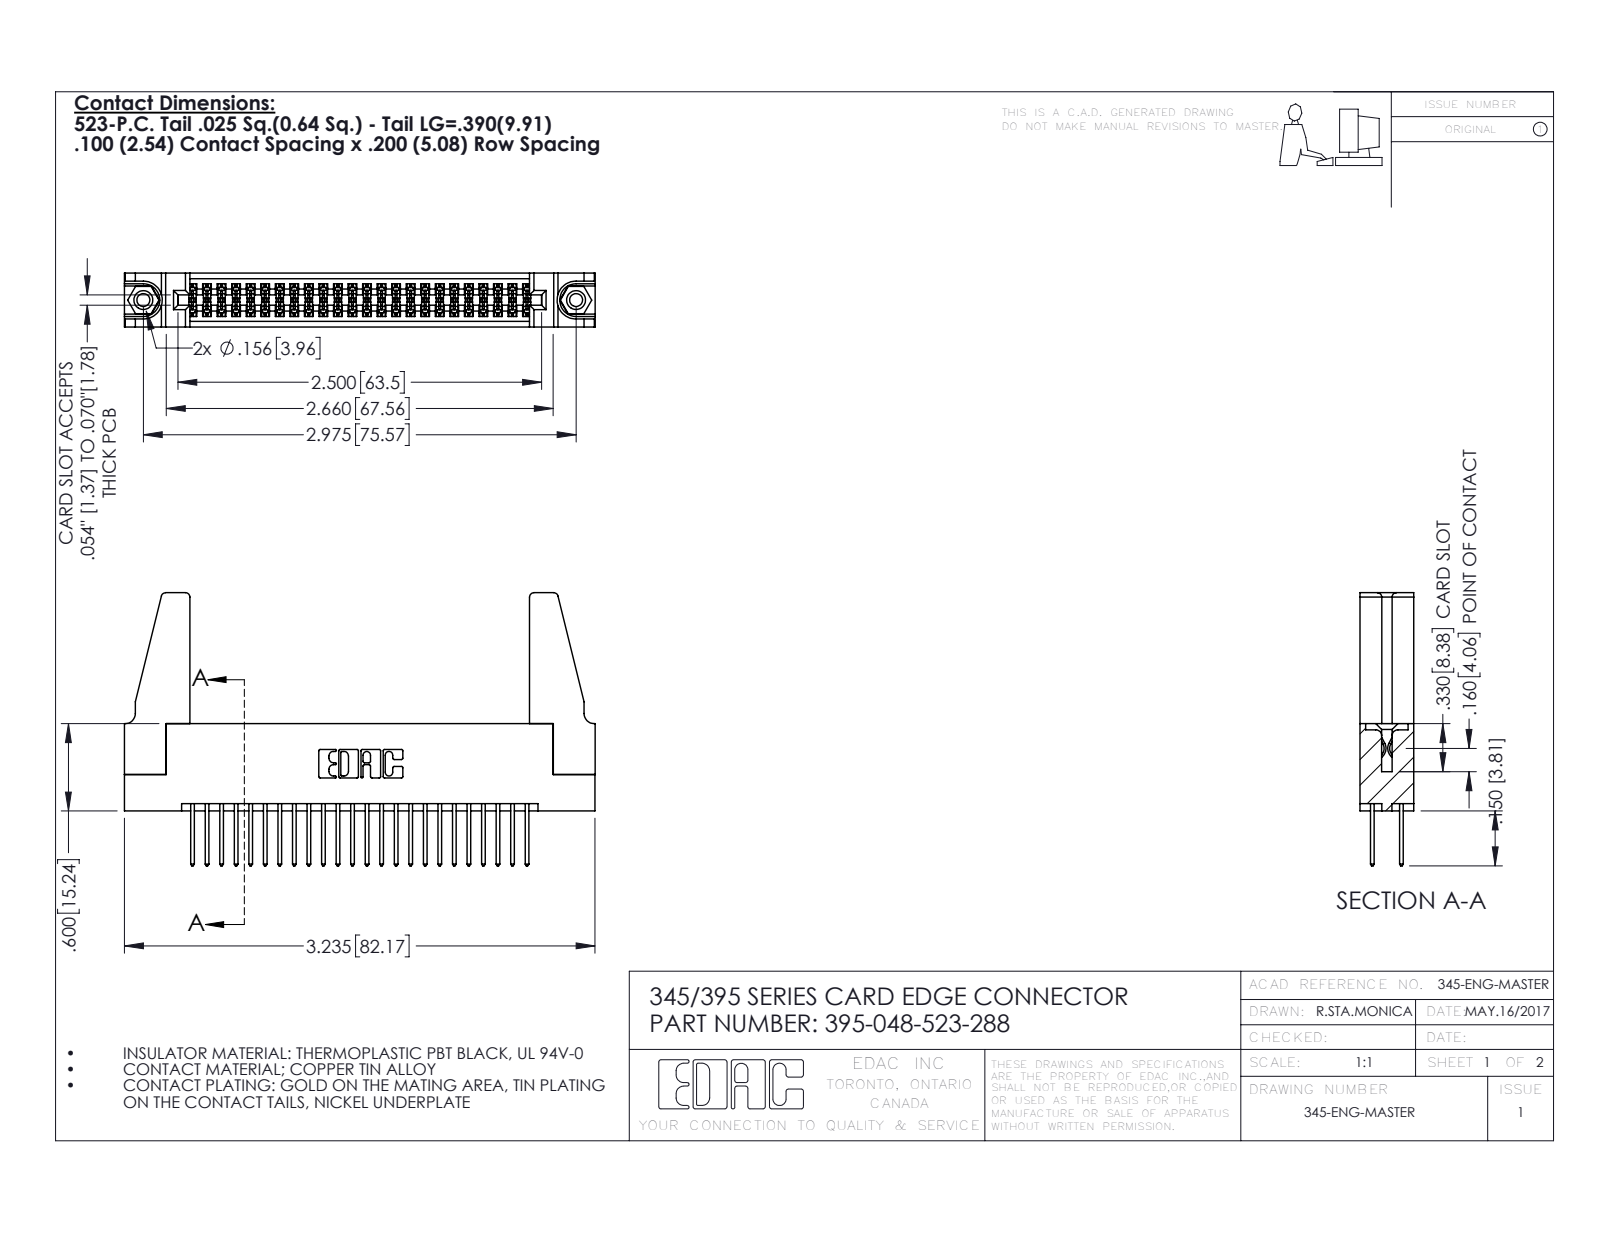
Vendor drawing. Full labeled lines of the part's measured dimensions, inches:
Part name (STEP PRODUCT): 395-048-523-288; 345-250-001_345-250-001-102; 345-220-078_345-220-088; 345 Part_Flush Mounting Lugs - 0.156 Dia-TH (+1 more)
STEP written by: SolidWorks 2016 (CONFIG_CONTROL_DESIGN)
Units: inches
Bodies: 53 solids, 2650 faces (1736 planar, 898 cylindrical, 16 other)
Overall size (bounding box): 3.236 × 1.877 × 0.37
Volume: 0.682 in³ · Surface area: 23.12 in²
Round holes (diameter × count): ⌀0.089 ×2, ⌀0.125 ×2, ⌀0.156 ×2, ⌀0.064 ×1
Round bosses / shafts (diameter × count): ⌀0.155 ×2
Partial cylindrical surfaces — rounded edges, fillets, slot ends (radius × count): R0.006 ×72, R0.01 ×48, R0.01 ×22, R0.03 ×8, R0.007 ×6, R0.031 ×6, R0.026 ×3, R0.014 ×2
Main face-to-face distances: 0.072, 0.298, 0.37, 0.2, 0.098, 0.272, 0.025, 0.225, 0.175, 0.149
Hole centre spacings: 0.27, 2.741, 2.975
